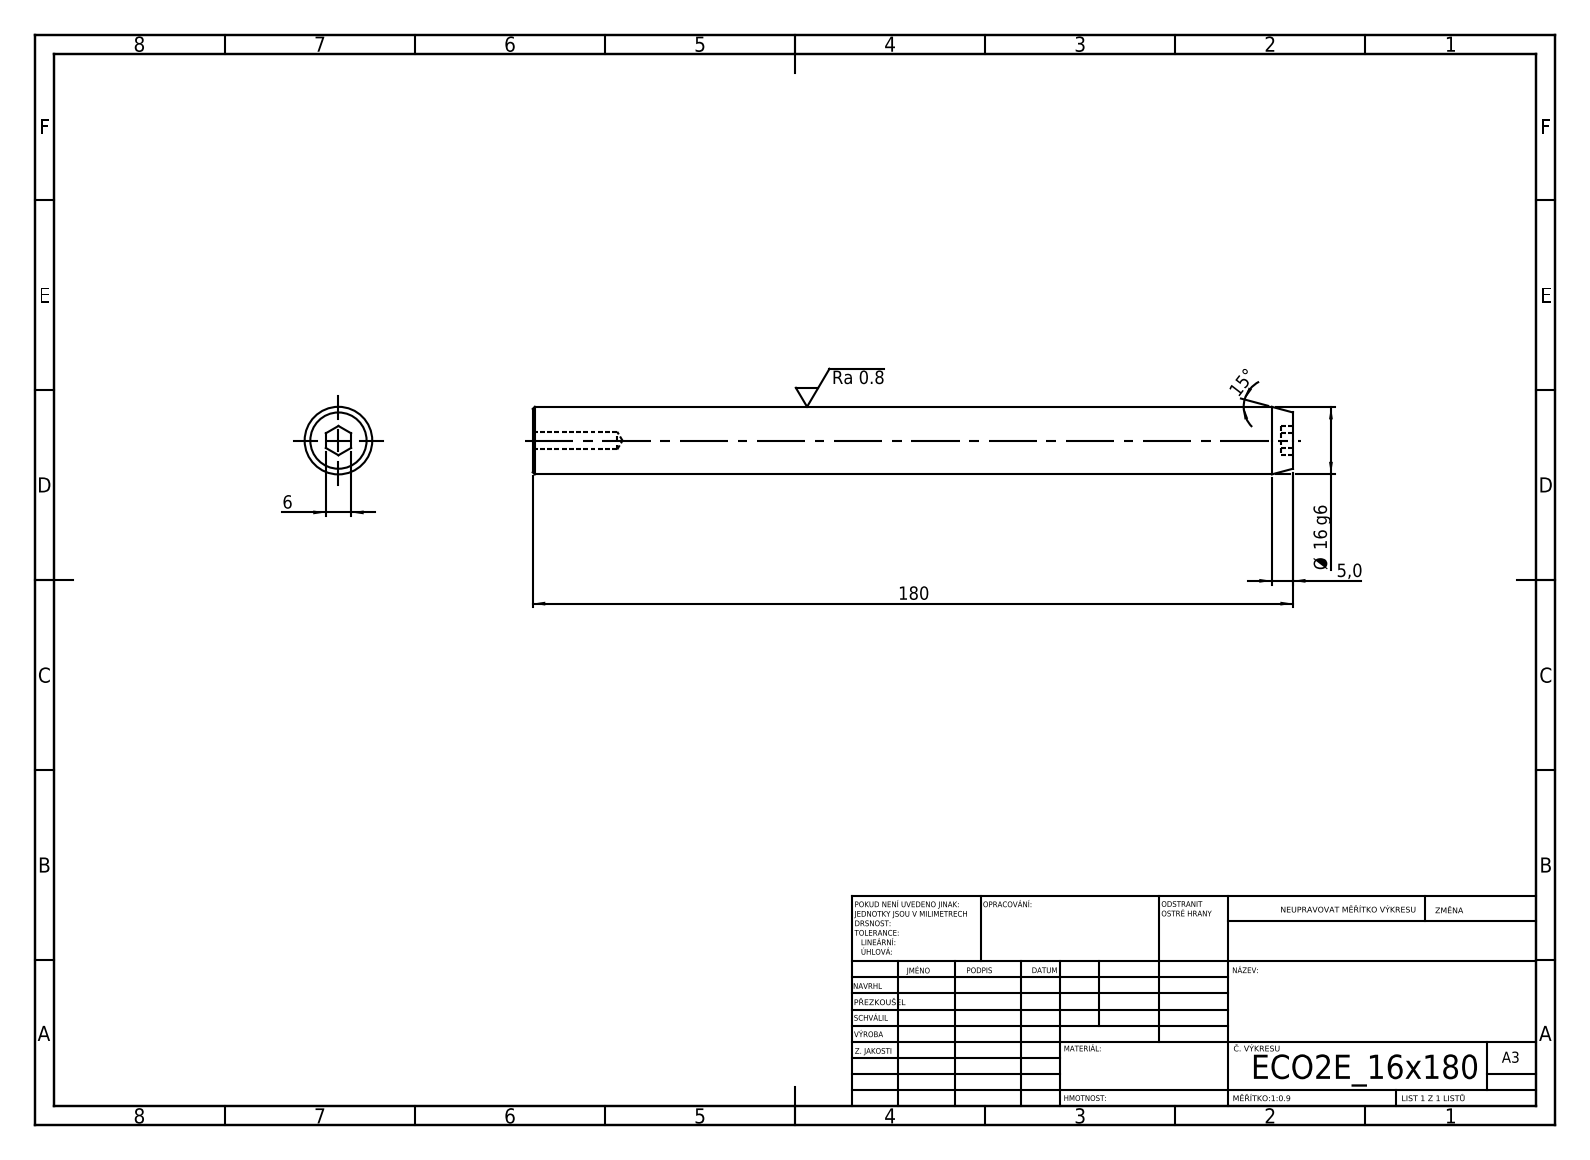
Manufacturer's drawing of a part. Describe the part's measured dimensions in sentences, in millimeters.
Its 3-D file was written by "SolidWorks 2019 (CONFIG_CONTROL_DESIGN)". It is 1 solid with 19 faces: 9 planar, 4 cylindrical and 6 other. Overall it measures 180 by 16 by 16 millimeters. Its volume is 35 656 cubic millimeters and its surface area 9 685 square millimeters. Round holes: 1 of diameter 4.2. Round bosses or shafts: 1 of diameter 16. The main face-to-face distances are 180, 2.8, 177.2, 6.
